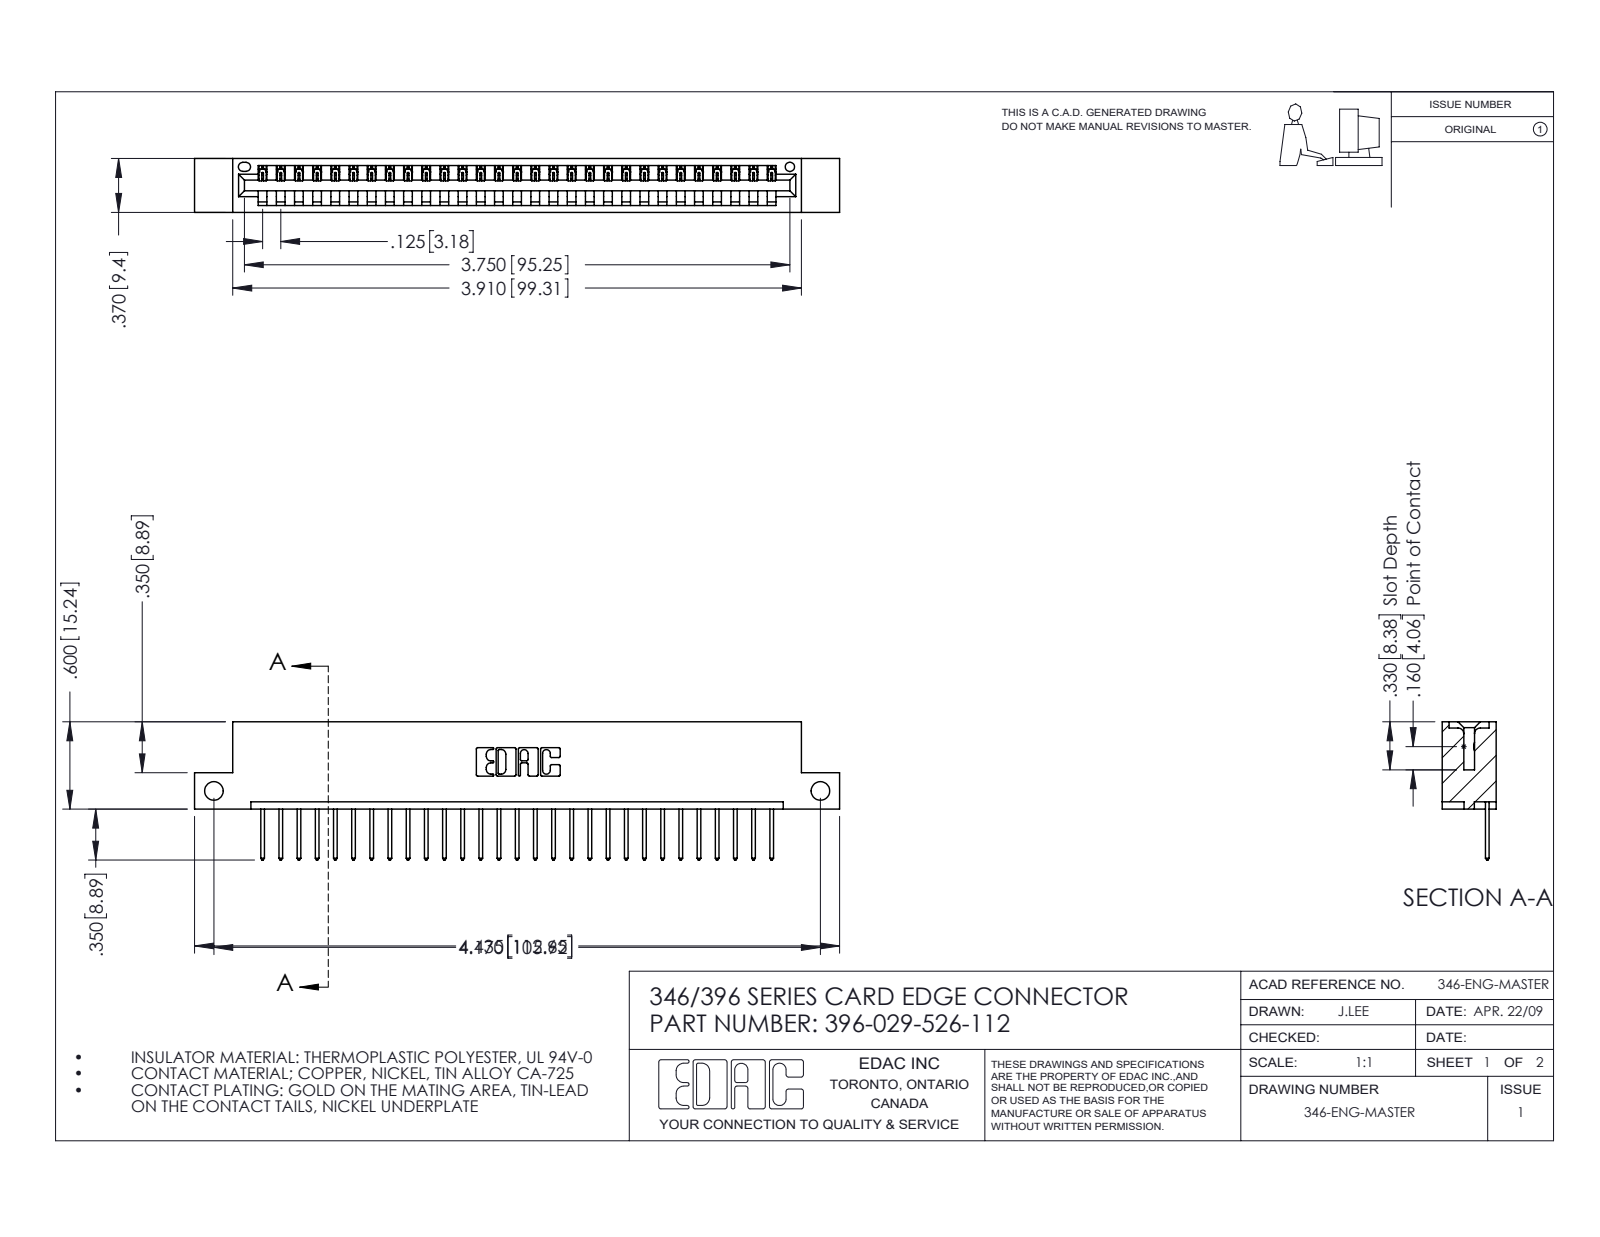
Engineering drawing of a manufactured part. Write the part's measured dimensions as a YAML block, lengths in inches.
part_name: "396-029-526-112; 345-292-001_345-293-126; 346 Part_Flush Mounting Lugs - Side Mount"
step_written_by: "SolidWorks 2016 (CONFIG_CONTROL_DESIGN)"
units: inches
bodies: {solids: 30, faces: 1804, planar: 1236, cylindrical: 568, other: 0}
overall_size: [4.435, 0.95, 0.37]
volume: 0.646
surface_area: 20.02
round_holes:
  - {diameter: 0.128, count: 2}
  - {diameter: 0.064, count: 1}
partial_cylinders:
  - {radius: 0.006, count: 58}
  - {radius: 0.01, count: 58}
  - {radius: 0.01, count: 22}
  - {radius: 0.007, count: 6}
  - {radius: 0.031, count: 6}
  - {radius: 0.026, count: 3}
  - {radius: 0.031, count: 2}
  - {radius: 0.04, count: 2}
face_to_face_distances: [0.048, 0.322, 0.25, 0.37, 0.072, 0.298, 0.025, 0.148, 0.222, 0.1]
hole_center_spacings: [4.17]
